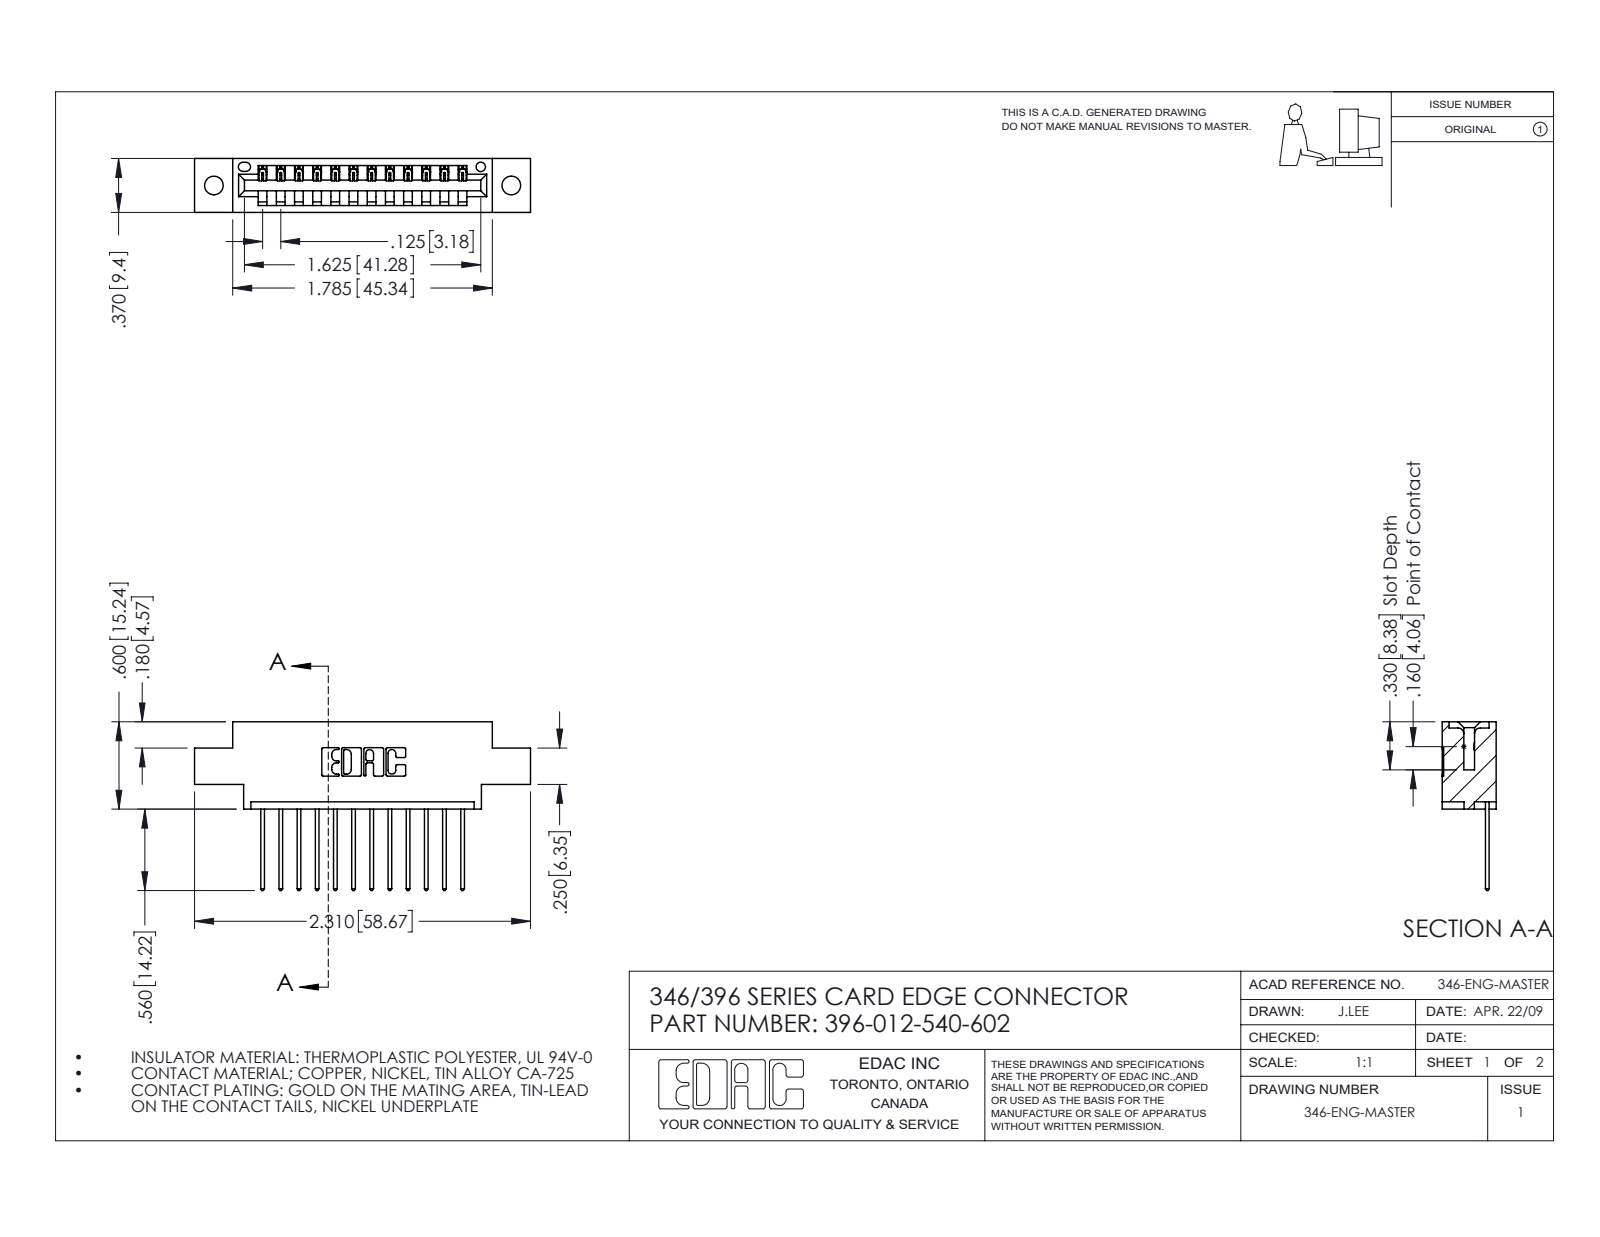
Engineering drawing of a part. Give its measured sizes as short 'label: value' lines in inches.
name: 346 Part_0.170 Offset - 0.128 Dia; 345-292-001_345-293-140; 396-012-540-602
written by: SolidWorks 2016 (CONFIG_CONTROL_DESIGN)
unit: in
bodies: 13 solids, 822 faces (560 planar, 262 cylindrical, 0 other)
size: 2.31 × 1.16 × 0.37
volume: 0.319 in³; area: 9.651 in²
holes: 2× ⌀0.128, 1× ⌀0.064
rounds: 24× R0.006, 24× R0.01, 22× R0.01, 6× R0.007, 6× R0.031, 3× R0.026, 2× R0.031, 2× R0.04
face distances: 0.25, 0.37, 0.048, 0.322, 0.072, 0.298, 0.025, 0.148, 0.222, 0.1
hole spacings: 0.246, 1.839, 2.045
